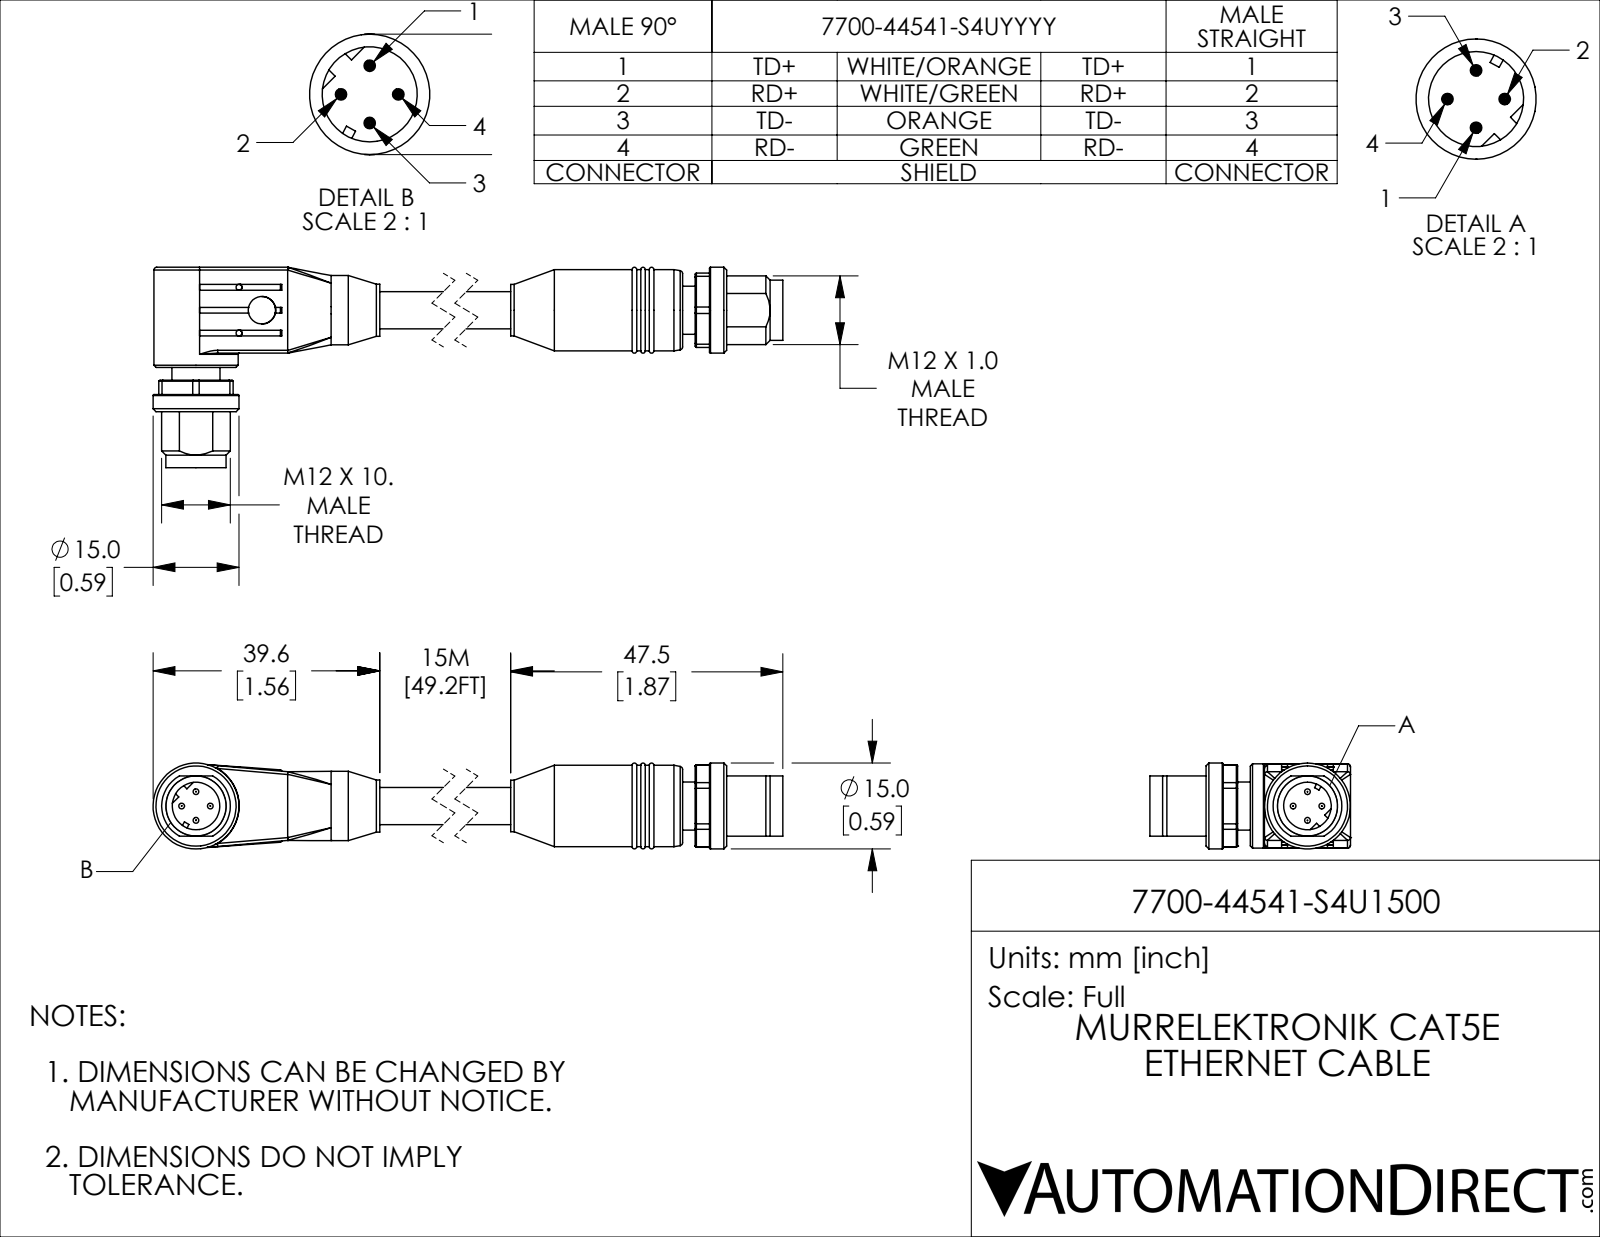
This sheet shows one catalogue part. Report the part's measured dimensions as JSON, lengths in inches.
{"part_name": "7700-44541-S4U1500_1; 7700-44541-S4U1500_2; 7700-44541-S4U1500", "step_written_by": "SolidWorks 2021 (CONFIG_CONTROL_DESIGN)", "units": "inches", "bodies": {"solids": 2, "faces": 284, "planar": 114, "cylindrical": 90, "other": 80}, "overall_size": [5.254, 1.378, 0.591], "volume_in3": 0.955, "surface_area_in2": 10.92, "round_holes": [[0.041, 4], [0.327, 2], [0.189, 1]], "round_bosses_or_shafts": [[0.039, 8], [0.591, 2], [0.413, 2], [0.331, 2], [0.579, 1], [0.559, 1], [0.476, 1], [0.358, 1]], "partial_cylinders_radius": [[0.02, 4], [0.012, 2], [0.236, 2], [0.283, 2]], "face_to_face_distances": [0.689, 0.087, 0.098, 0.185, 0.591, 0.035, 0.252, 0.339, 0.217, 0.303], "hole_center_spacings": [0.315]}
